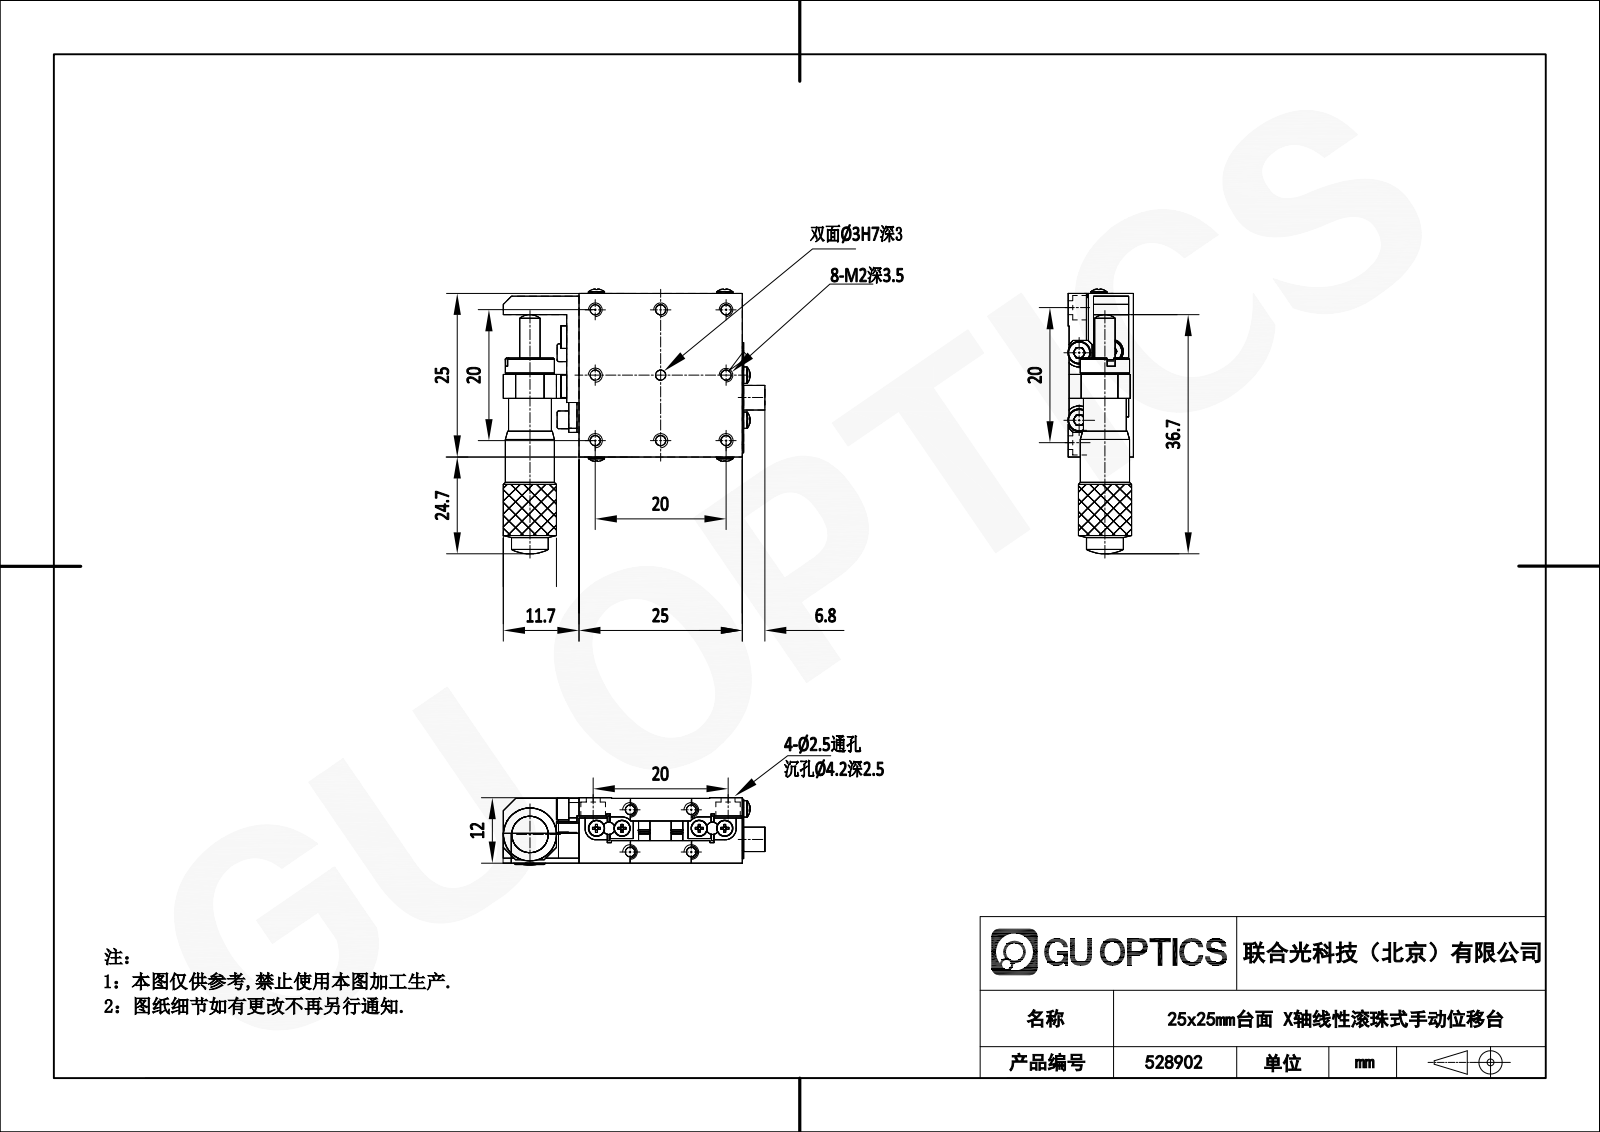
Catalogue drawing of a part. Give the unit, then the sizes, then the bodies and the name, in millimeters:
Units: millimetres
Overall size (bounding box): 50.8 × 43.16 × 14.68
Round holes (diameter × count): ⌀3.8 ×6, ⌀3 ×2
Round bosses / shafts (diameter × count): ⌀1.57 ×8, ⌀4.2 ×6, ⌀2.5 ×4, ⌀6 ×2, ⌀3.8 ×2, ⌀9.12 ×1, ⌀8.42 ×1, ⌀8 ×1
Partial cylindrical surfaces — rounded edges, fillets, slot ends (radius × count): R1.32 ×8, R1 ×4, R1.1 ×2, R1.2 ×2
Main face-to-face distances: 11.8, 3.6, 8.2, 4.7, 25, 4, 15, 5.3, 12, 3.5
Hole centre spacings: 5.4, 6.5, 15, 9.6, 13, 20.4
Bodies: 0 solids, 2141 faces (139 planar, 458 cylindrical, 1544 other)
Part name (STEP PRODUCT): 528902
STEP written by: SolidWorks 2020 (CONFIG_CONTROL_DESIGN)
